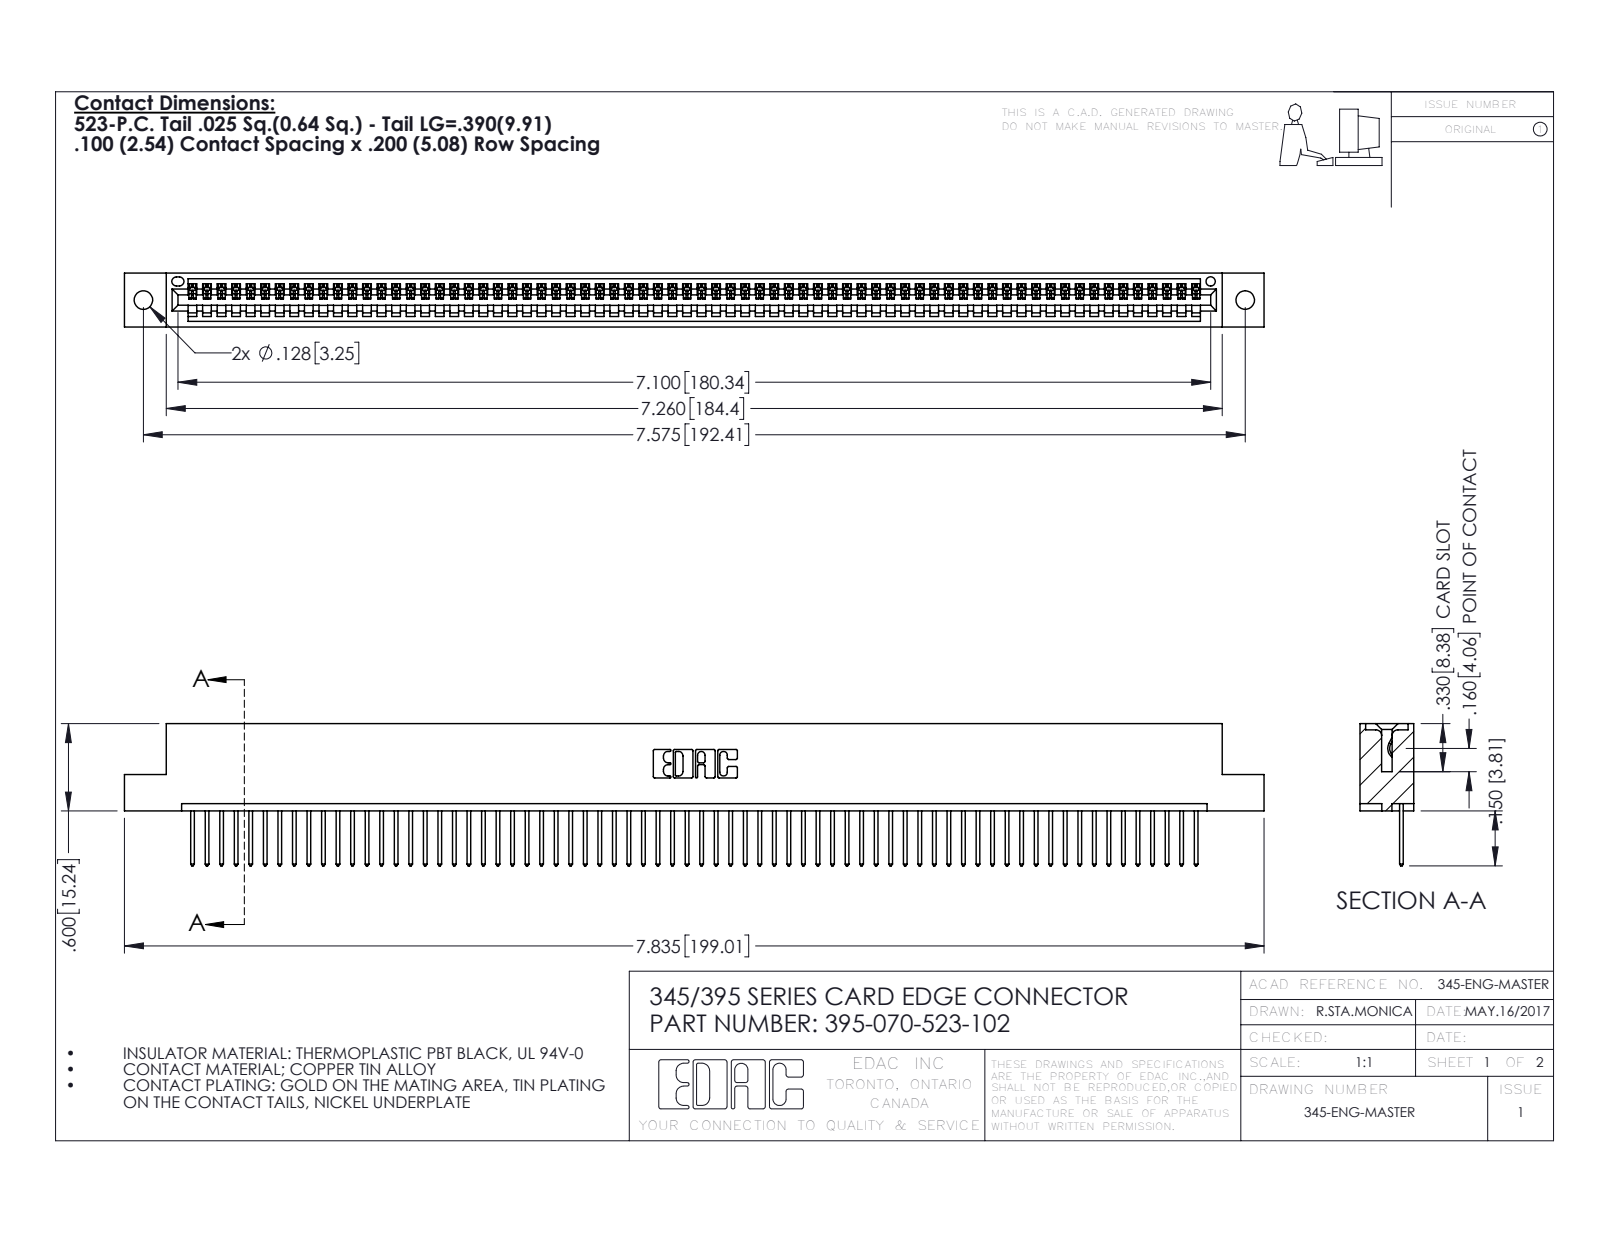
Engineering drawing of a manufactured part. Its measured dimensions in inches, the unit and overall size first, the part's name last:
Units: inches
Overall size (bounding box): 7.835 × 0.977 × 0.37
Round holes (diameter × count): ⌀0.128 ×2, ⌀0.064 ×1
Partial cylindrical surfaces — rounded edges, fillets, slot ends (radius × count): R0.006 ×140, R0.01 ×140, R0.01 ×22, R0.007 ×6, R0.031 ×6, R0.026 ×3, R0.031 ×2, R0.04 ×2
Main face-to-face distances: 0.298, 0.072, 0.37, 0.2, 0.098, 0.272, 0.025, 0.225, 0.149, 0.072
Hole centre spacings: 0.27, 7.339, 7.575
Volume: 1.164 in³ · Surface area: 39.56 in²
Bodies: 71 solids, 4186 faces (2880 planar, 1306 cylindrical, 0 other)
Part name (STEP PRODUCT): 395-070-523-102; 345-292-001_345-293-123; 345 Part_Flush Mounting Lugs - 0.128 Dia
STEP written by: SolidWorks 2016 (CONFIG_CONTROL_DESIGN)
